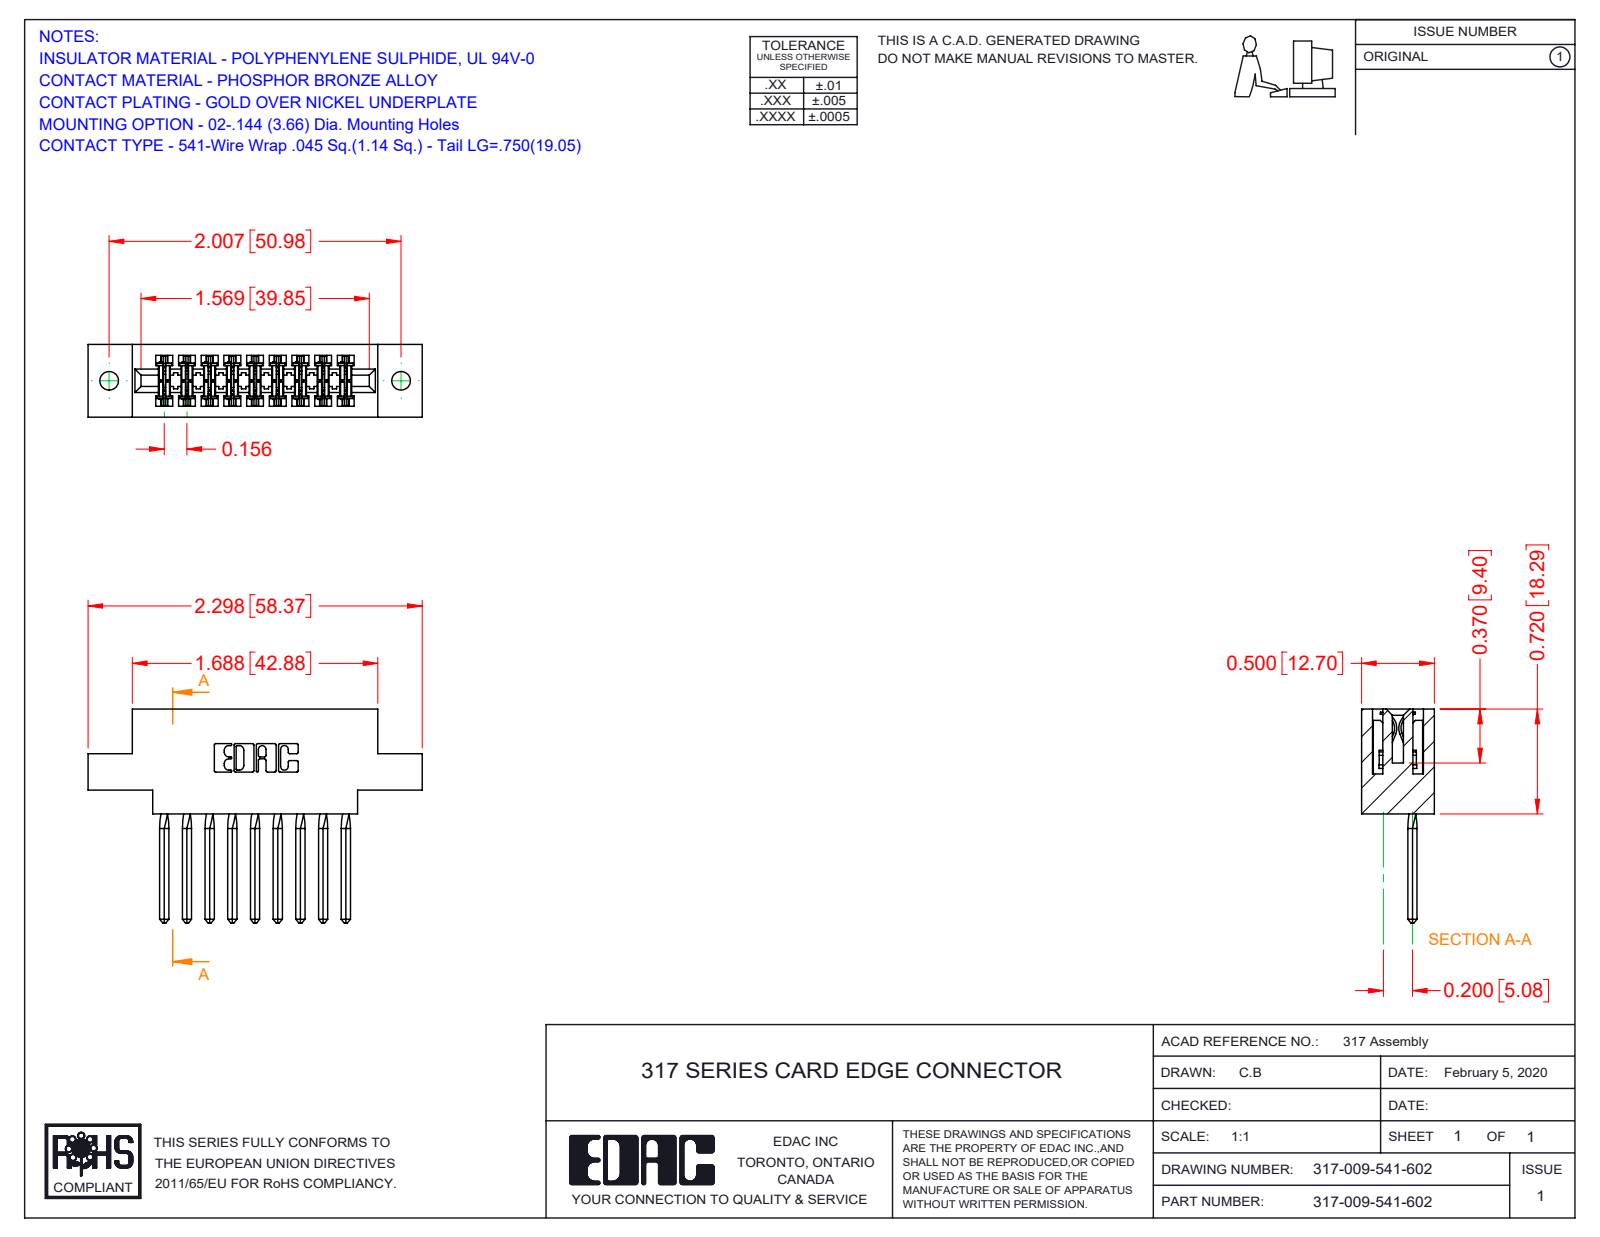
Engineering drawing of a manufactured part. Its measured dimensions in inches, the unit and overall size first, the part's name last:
Units: inches
Overall size (bounding box): 2.298 × 1.47 × 0.5
Round holes (diameter × count): ⌀0.128 ×2
Partial cylindrical surfaces — rounded edges, fillets, slot ends (radius × count): R0.01 ×22, R0.015 ×18, R0.007 ×6, R0.031 ×6, R0.026 ×3, R0.095 ×2, R0.1 ×2, R0.11 ×2
Main face-to-face distances: 0.5, 0.075, 0.425, 0.11, 0.065, 0.22, 0.156, 0.331, 0.35, 0.116
Hole centre spacings: 2.007
Volume: 0.513 in³ · Surface area: 16.31 in²
Bodies: 10 solids, 1470 faces (1174 planar, 260 cylindrical, 36 other)
Part name (STEP PRODUCT): 317 Part_.144 Dia; 317-290-002_541; 317-009-541-602
STEP written by: SolidWorks 2016 (CONFIG_CONTROL_DESIGN)
